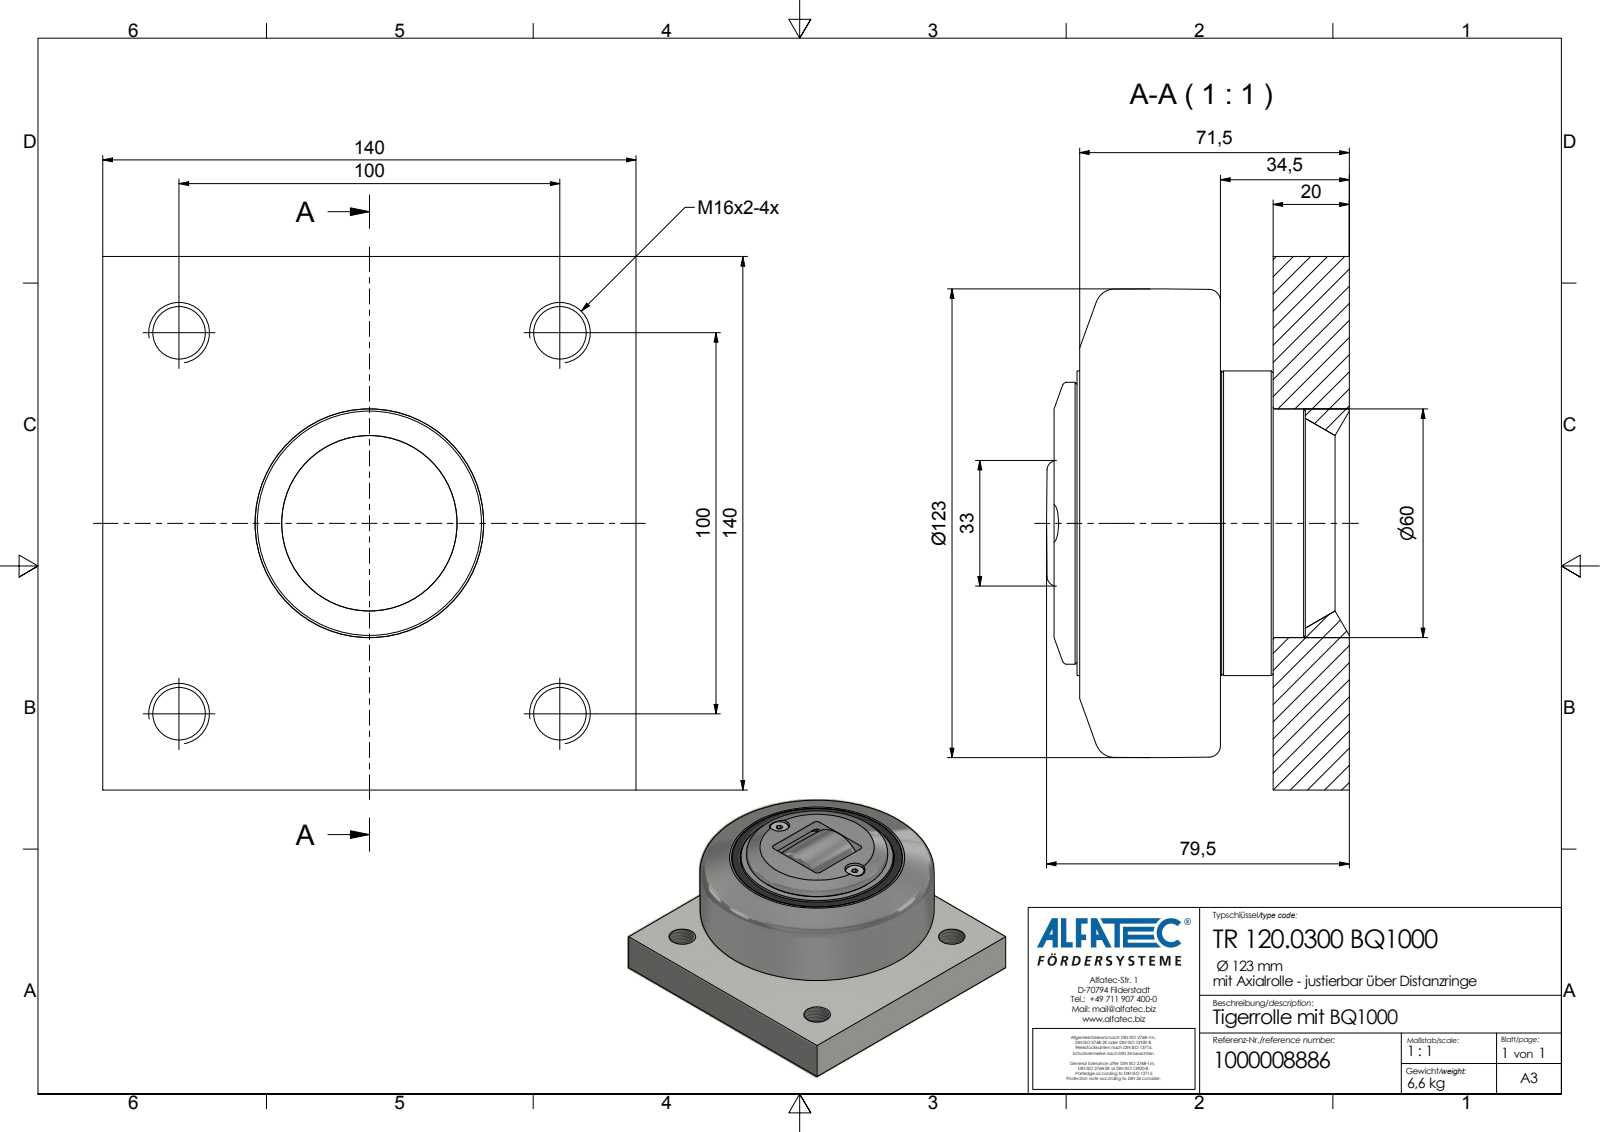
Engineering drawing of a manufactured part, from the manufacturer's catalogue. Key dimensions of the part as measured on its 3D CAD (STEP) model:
Part name (STEP PRODUCT): TR 120.0300 BQ1000_Kontur
STEP written by: Autodesk Inventor 2020 (AUTOMOTIVE_DESIGN)
Units: millimetres
Bodies: 2 solids, 126 faces (52 planar, 45 cylindrical, 29 other)
Overall size (bounding box): 140 × 140 × 79.5
Volume: 800 237 mm³ · Surface area: 131 725 mm²
Round holes (diameter × count): ⌀13.84 ×4, ⌀5.5 ×2, ⌀10.5 ×2, ⌀3 ×1, ⌀26 ×1, ⌀28 ×1, ⌀71.4 ×1, ⌀81 ×1, ⌀87 ×1, ⌀89.5 ×1, ⌀95 ×1
Round bosses / shafts (diameter × count): ⌀9.75 ×2, ⌀5 ×2, ⌀86.8 ×1, ⌀84.5 ×1, ⌀80 ×1, ⌀79 ×1, ⌀74 ×1, ⌀71 ×1
Partial cylindrical surfaces — rounded edges, fillets, slot ends (radius × count): R2 ×4, R19 ×1
Main face-to-face distances: 20, 140, 33.8, 13.8, 71.5, 51.5, 37.7, 30.5, 5.5, 6.5
Hole centre spacings: 54.63, 70.71, 92.65, 100, 28, 141.42, 7.7, 56
